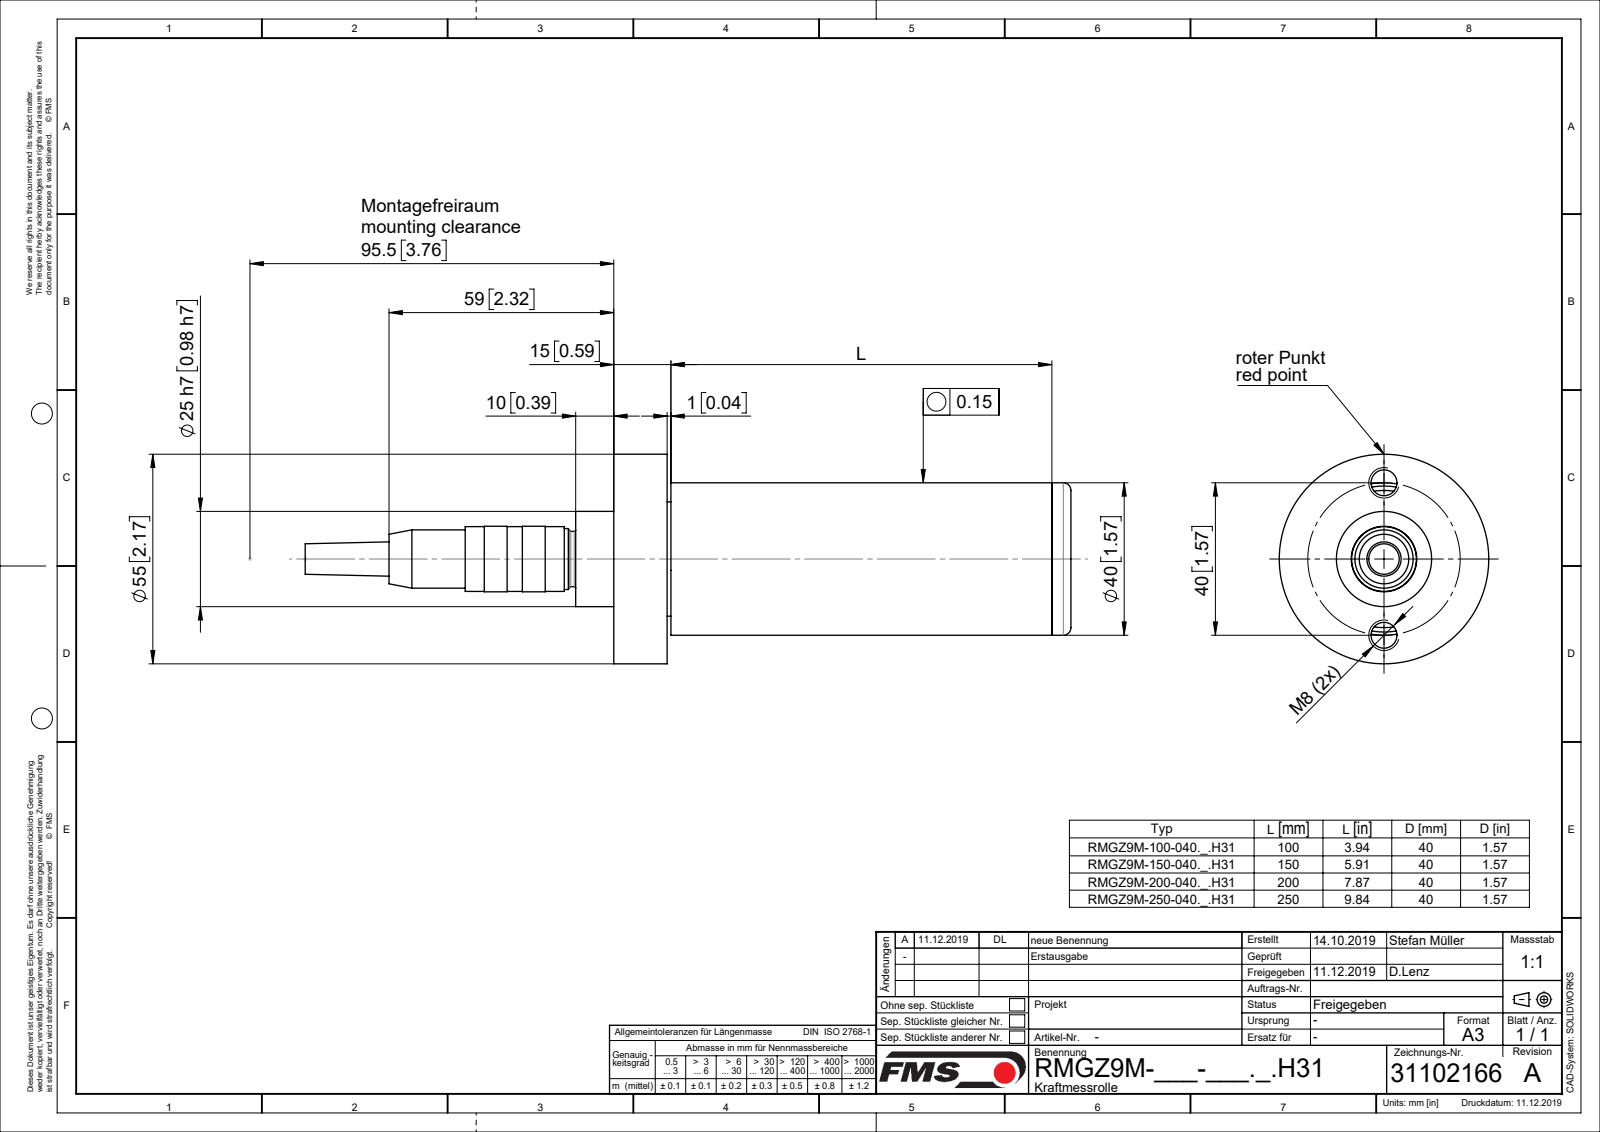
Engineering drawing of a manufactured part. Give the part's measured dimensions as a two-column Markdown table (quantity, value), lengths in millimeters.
| quantity | value |
| --- | --- |
| part name | R48618; R4862004; TEIL1; RILLENKUGELLAGER_6201 (+4 more) |
| STEP written by | Mechanical Desktop 2007 (CONFIG_CONTROL_DESIGN) |
| units | millimeters |
| bodies | 7 solids, 225 faces (63 planar, 100 cylindrical, 62 other) |
| overall size | 201 × 55 × 55 |
| volume | 132 686 mm³ |
| surface area | 60 478 mm² |
| round holes (diameter × count) | 6.91 × 2, 10 × 1, 11.5 × 1, 12 × 1, 13.3 × 1, 14 × 1, 26.3 × 1, 27 × 1, 28 × 1, 32 × 1, 35 × 1 |
| round bosses / shafts (diameter × count) | 55 × 1, 40 × 1, 31.3 × 1, 25 × 1, 17.5 × 1, 17.2 × 1, 17 × 1, 16 × 1 |
| partial cylindrical surfaces (radius × count) | 10.5 × 1 |
| main face-to-face distances | 14, 16, 7.4, 2.6, 14.5, 4.5, 119.5, 105.5, 30, 10 |
| hole center spacings | 20, 40 |
